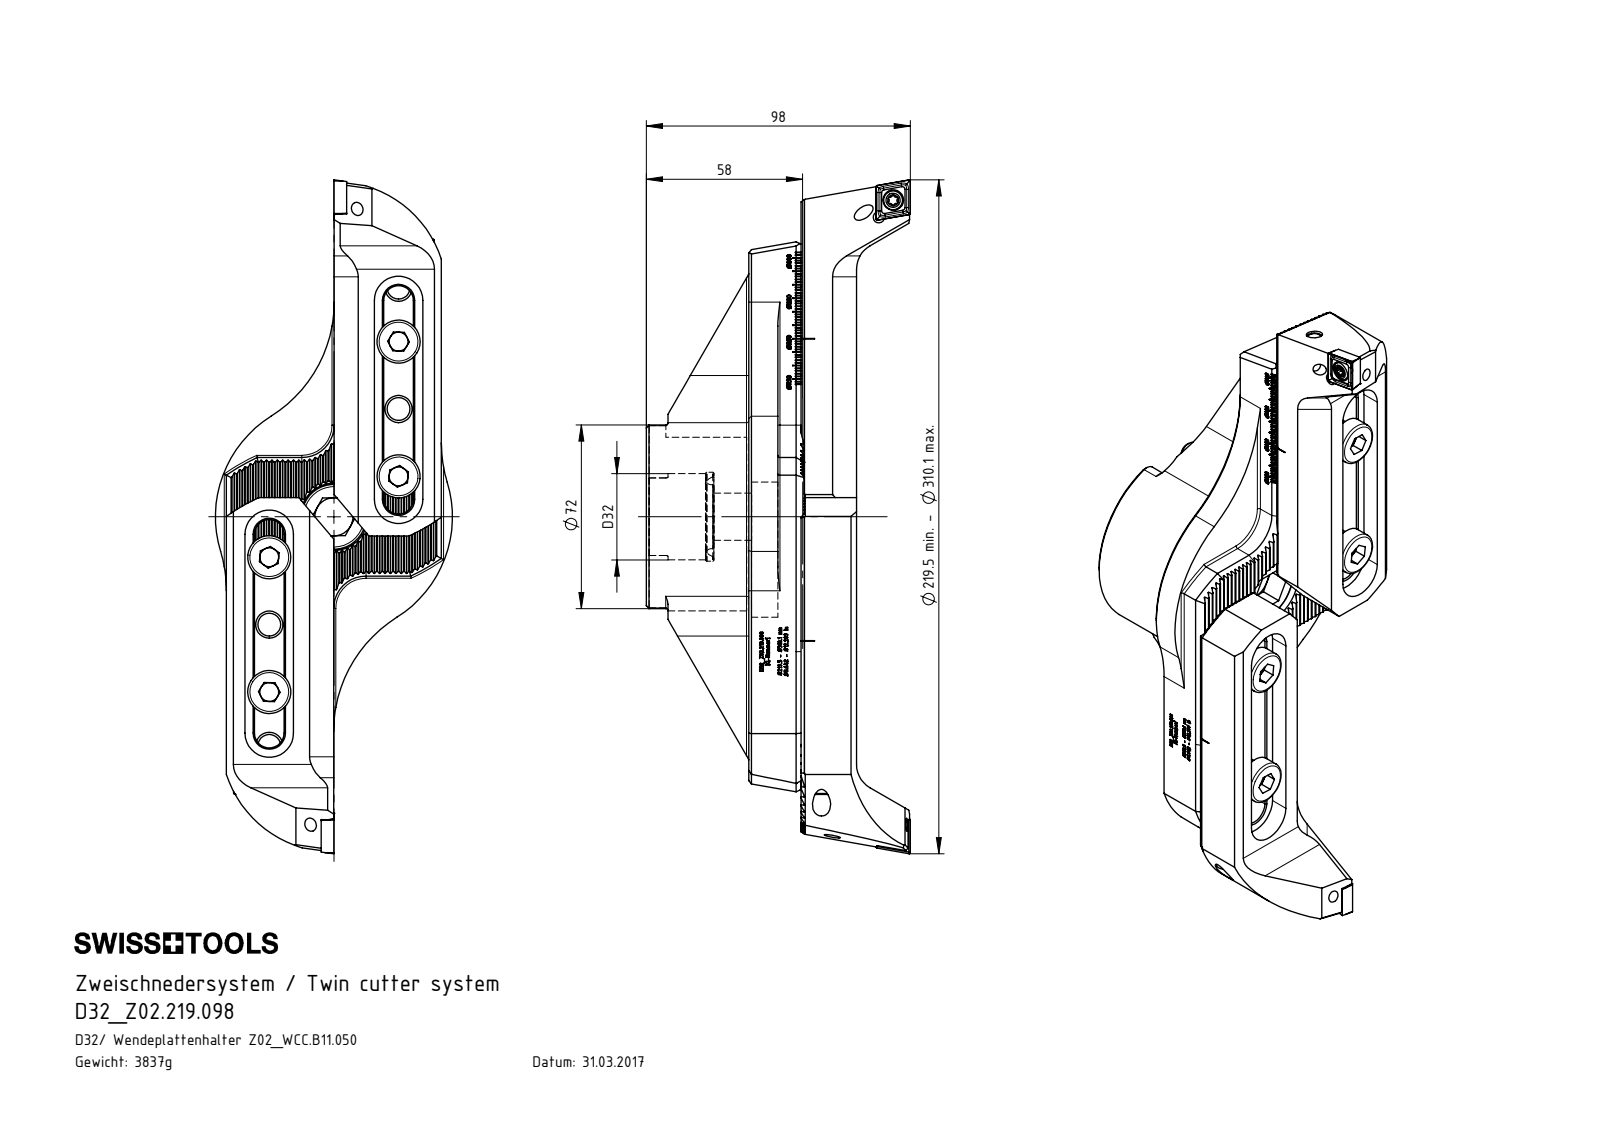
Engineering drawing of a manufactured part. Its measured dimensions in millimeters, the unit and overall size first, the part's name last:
Units: millimetres
Overall size (bounding box): 277.9 × 218.5 × 100
Round holes (diameter × count): ⌀5 ×19, ⌀4.2 ×8, ⌀8.5 ×8, ⌀6.8 ×6, ⌀12 ×4, ⌀10 ×3, ⌀5.5 ×2, ⌀6 ×2, ⌀6.5 ×2, ⌀7.6 ×2, ⌀14 ×1, ⌀17 ×1
Round bosses / shafts (diameter × count): ⌀6 ×8, ⌀16 ×5, ⌀10 ×4, ⌀14 ×2, ⌀7 ×2, ⌀5 ×2, ⌀4.6 ×2, ⌀100 ×1
Partial cylindrical surfaces — rounded edges, fillets, slot ends (radius × count): R0.14 ×79, R0.5 ×14, R0.39 ×12, R5.5 ×8, R10 ×8, R0.69 ×6, R0.69 ×6, R1.9 ×6
Main face-to-face distances: 40, 1.73, 38, 8.66, 6.93, 17.32, 15.59, 10.39, 3.46, 39.8
Hole centre spacings: 25, 93.3, 8.21, 8.33, 10.96, 12.25, 13, 16.45
Volume: 1 168 000 mm³ · Surface area: 205 849 mm²
Bodies: 25 solids, 2904 faces (1515 planar, 553 cylindrical, 836 other)
Part name (STEP PRODUCT): HA0-D32.K01.130_A_Fertigbearbeitung; WCC-ER2.001.010_A; D32-ER2.001.022_B; Zylinderstift Ø6x12 (+8 more)
STEP written by: SolidWorks 2015 (CONFIG_CONTROL_DESIGN)
